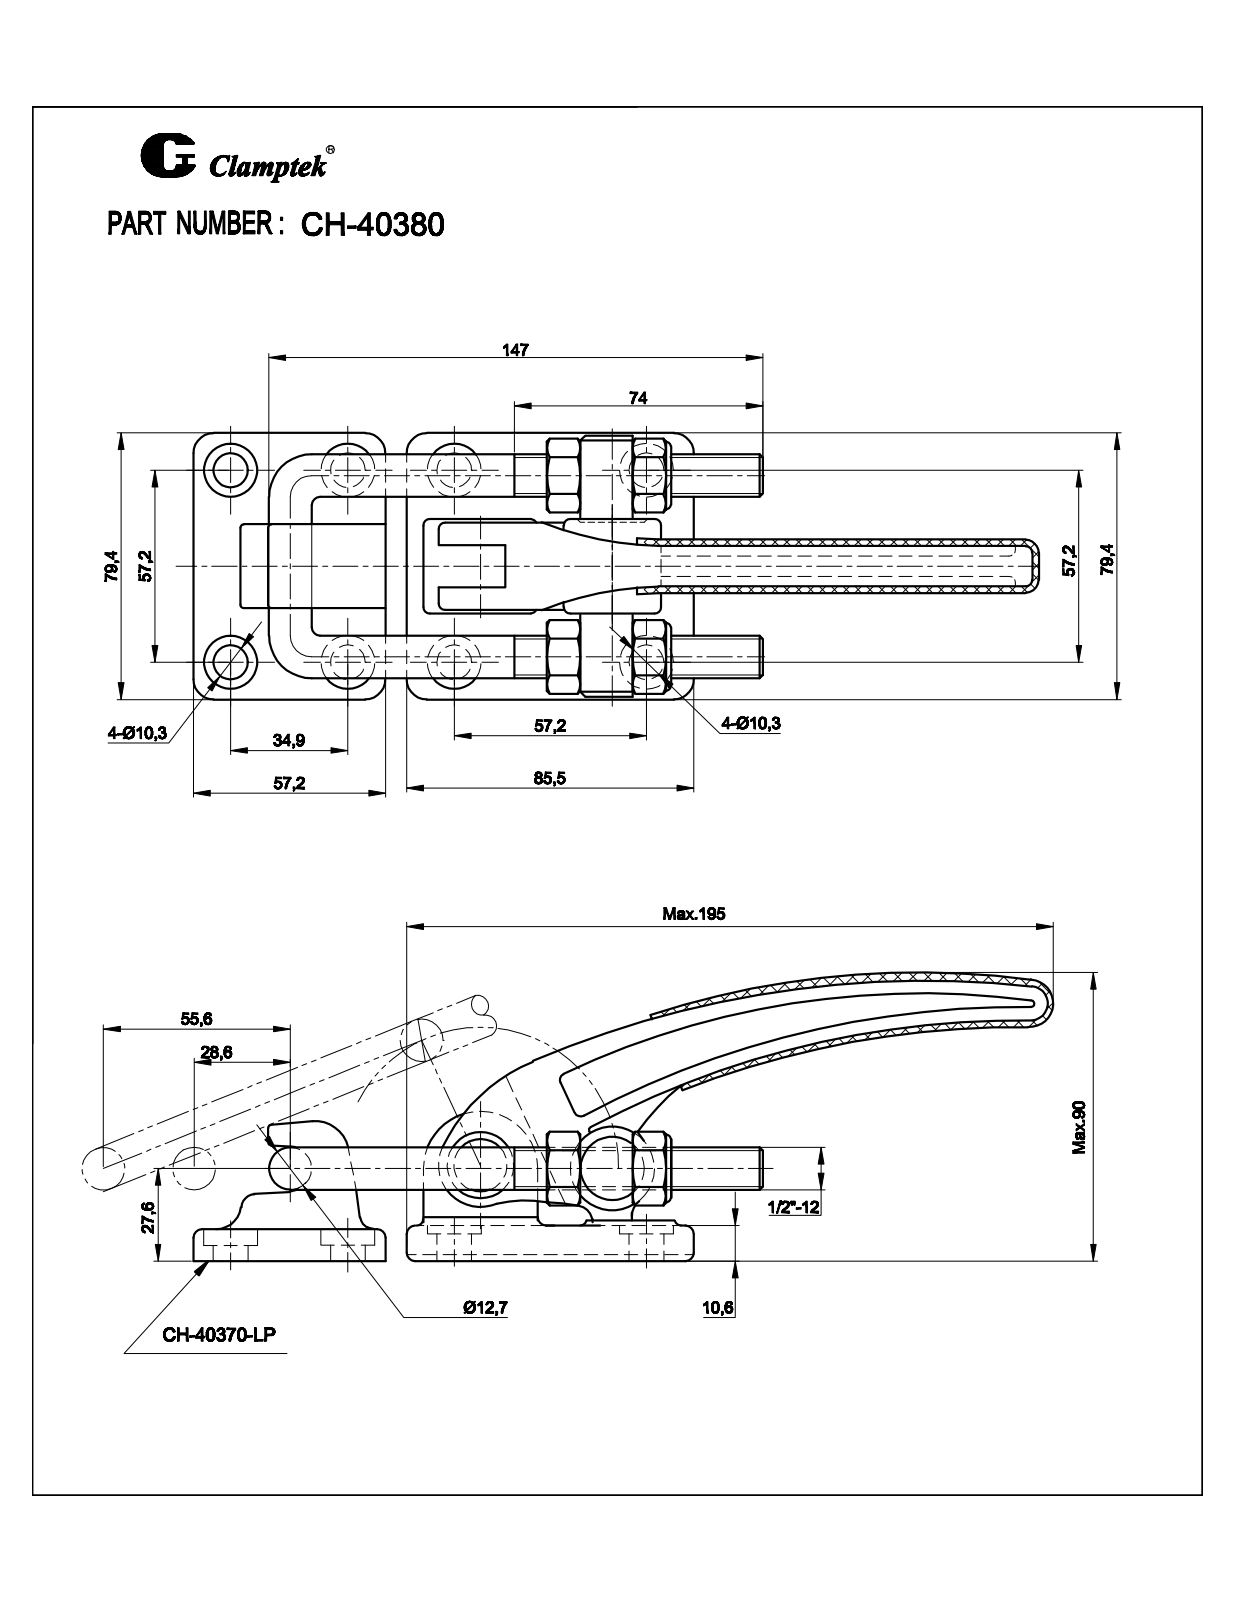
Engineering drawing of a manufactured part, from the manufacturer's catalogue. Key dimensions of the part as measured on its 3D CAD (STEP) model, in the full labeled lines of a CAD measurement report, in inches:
Part name (STEP PRODUCT): CH-40380; 1-2防栓螺母_默认
STEP written by: SolidWorks 2008 (CONFIG_CONTROL_DESIGN)
Units: inches
Bodies: 11 solids, 1373 faces (713 planar, 337 cylindrical, 323 other)
Overall size (bounding box): 10.407 × 3.367 × 3.156
Volume: 16.33 in³ · Surface area: 142.2 in²
Round holes (diameter × count): ⌀0.406 ×8, ⌀0.63 ×8, ⌀0.413 ×4, ⌀0.089 ×1, ⌀0.492 ×1, ⌀0.622 ×1, ⌀0.748 ×1
Round bosses / shafts (diameter × count): ⌀0.512 ×3, ⌀0.63 ×2, ⌀0.744 ×1, ⌀0.078 ×1
Partial cylindrical surfaces — rounded edges, fillets, slot ends (radius × count): R0.039 ×29, R0.059 ×11, R0.157 ×4, R0.236 ×4, R0.012 ×3, R1.969 ×2, R3.925 ×2, R0.244 ×1
Main face-to-face distances: 0.059, 0.417, 0.413, 0.354, 0.358, 0.217, 0.27, 0.754, 0.053, 0.807
Hole centre spacings: 2.252, 2.126, 1.374, 2.288, 2.638, 3.185, 3.21, 3.662
